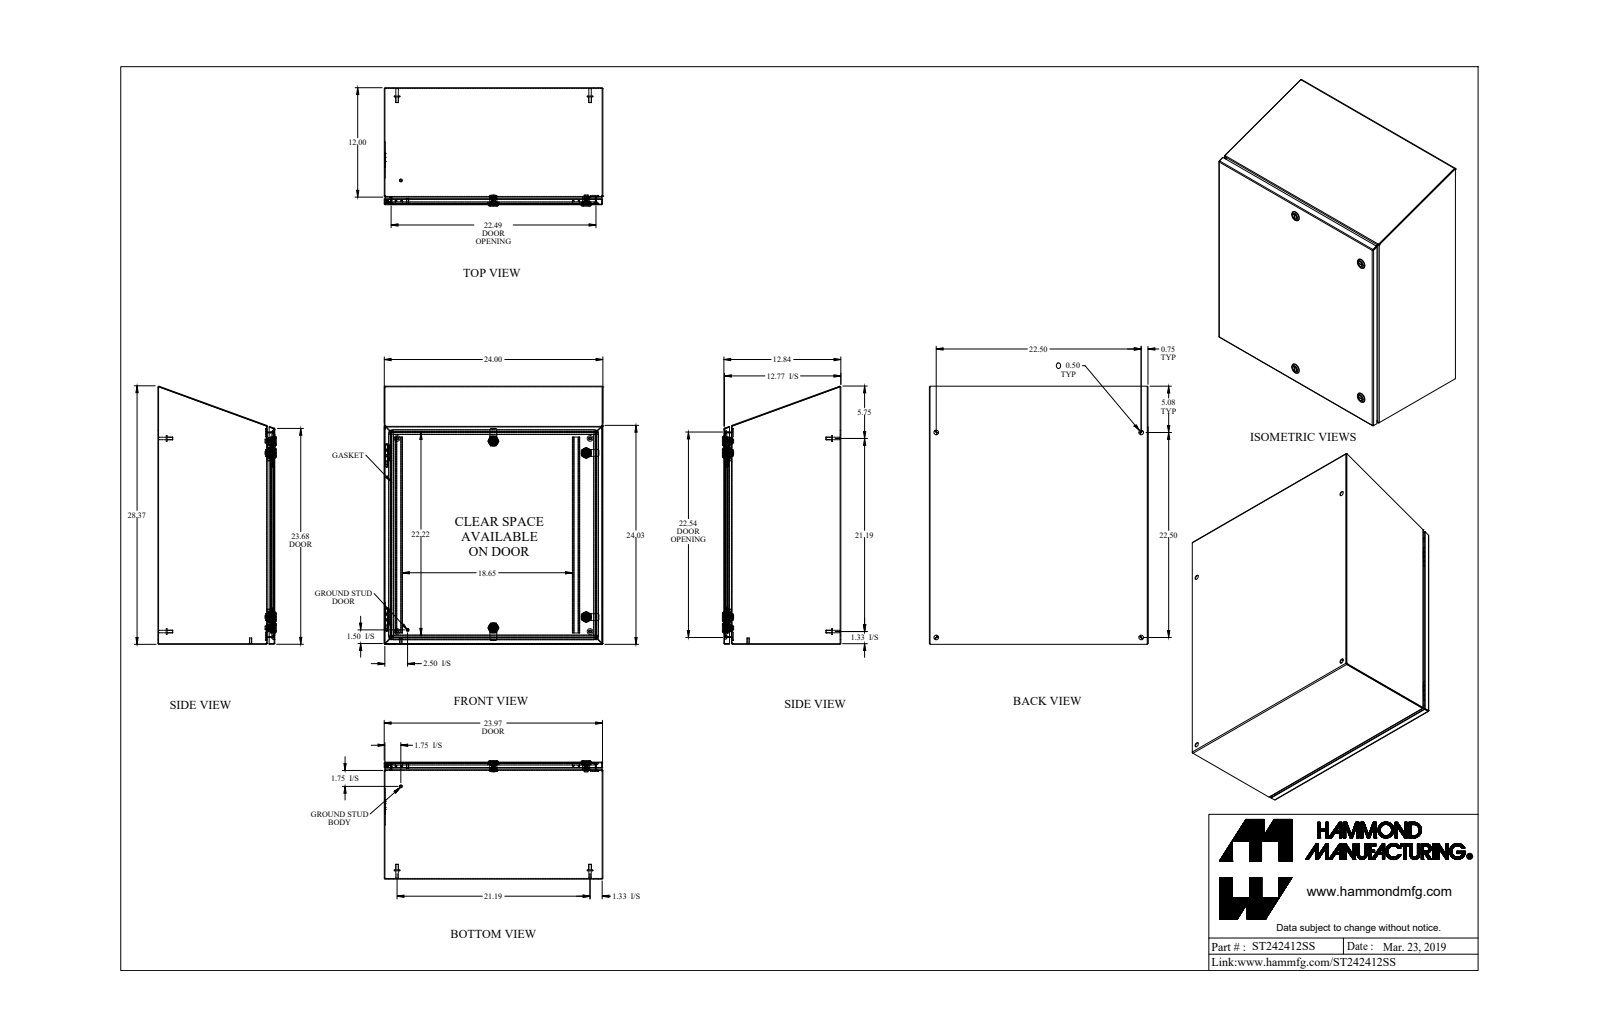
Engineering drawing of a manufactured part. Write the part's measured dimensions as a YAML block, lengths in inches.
part_name: "ST242412SS"
step_written_by: "SolidWorks 2018 (AUTOMOTIVE_DESIGN)"
units: inches
bodies: {solids: 41, faces: 1014, planar: 564, cylindrical: 310, other: 140}
overall_size: [28.328, 24.008, 12.997]
volume: 204.8
surface_area: 5726
round_holes:
  - {diameter: 0.5, count: 8}
  - {diameter: 0.197, count: 4}
  - {diameter: 0.387, count: 4}
  - {diameter: 0.63, count: 4}
  - {diameter: 0.768, count: 4}
  - {diameter: 0.172, count: 1}
  - {diameter: 0.24, count: 1}
  - {diameter: 0.242, count: 1}
round_bosses_or_shafts:
  - {diameter: 0.625, count: 8}
  - {diameter: 0.313, count: 6}
  - {diameter: 1.1, count: 4}
  - {diameter: 0.525, count: 4}
  - {diameter: 0.275, count: 4}
  - {diameter: 0.236, count: 4}
  - {diameter: 0.785, count: 3}
  - {diameter: 0.25, count: 2}
partial_cylinders:
  - {radius: 0.036, count: 18}
  - {radius: 0.108, count: 18}
  - {radius: 0.01, count: 12}
  - {radius: 0.048, count: 12}
  - {radius: 0.125, count: 8}
  - {radius: 0.188, count: 6}
  - {radius: 0.006, count: 4}
  - {radius: 0.062, count: 4}
face_to_face_distances: [0.072, 12.765, 12.693, 23.928, 12.837, 23.856, 24, 11.928, 0.837, 0.765]
hole_center_spacings: [22.5, 31.82, 2.497, 2.499, 10.258, 10.271, 11.267, 11.277]
